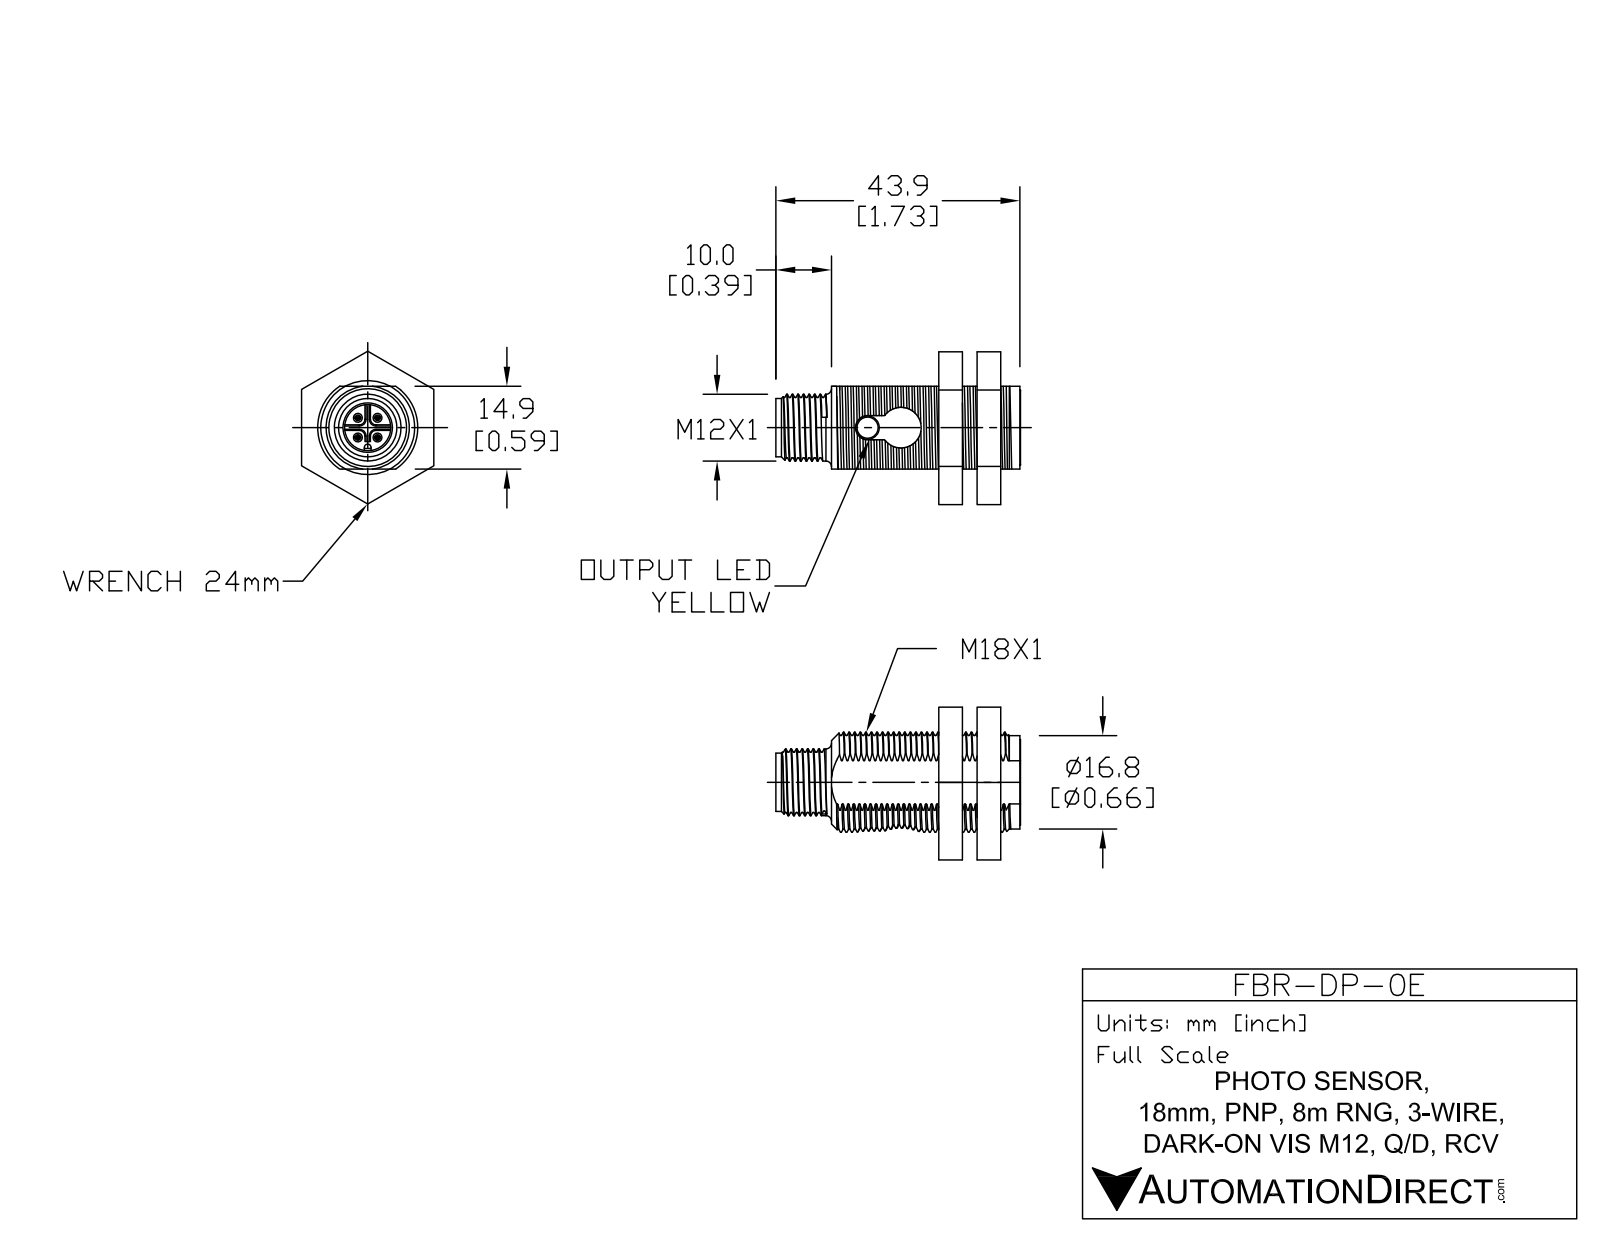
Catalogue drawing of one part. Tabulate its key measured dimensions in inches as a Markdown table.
| quantity | value |
| --- | --- |
| part name | FBR-DP-0E |
| STEP written by | SolidWorks 2011 (AUTOMOTIVE_DESIGN) |
| units | inches |
| bodies | 7 solids, 226 faces (131 planar, 30 cylindrical, 65 other) |
| overall size | 1.728 × 1.09 × 0.967 |
| volume | 0.628 in³ |
| surface area | 7.989 in² |
| round holes (diameter × count) | 0.093 × 1, 0.168 × 1, 0.285 × 1, 0.331 × 1 |
| round bosses / shafts (diameter × count) | 0.039 × 4, 0.472 × 1, 0.409 × 1 |
| partial cylindrical surfaces (radius × count) | 0.254 × 2, 0.294 × 2, 0.02 × 1, 0.331 × 1, 0.335 × 1, 0.354 × 1 |
| main face-to-face distances | 0.315, 0.177, 0.945, 0.591, 0.039, 0.492, 0.232, 0.547, 0.409, 0.724 |
| hole center spacings | 0.26 |
